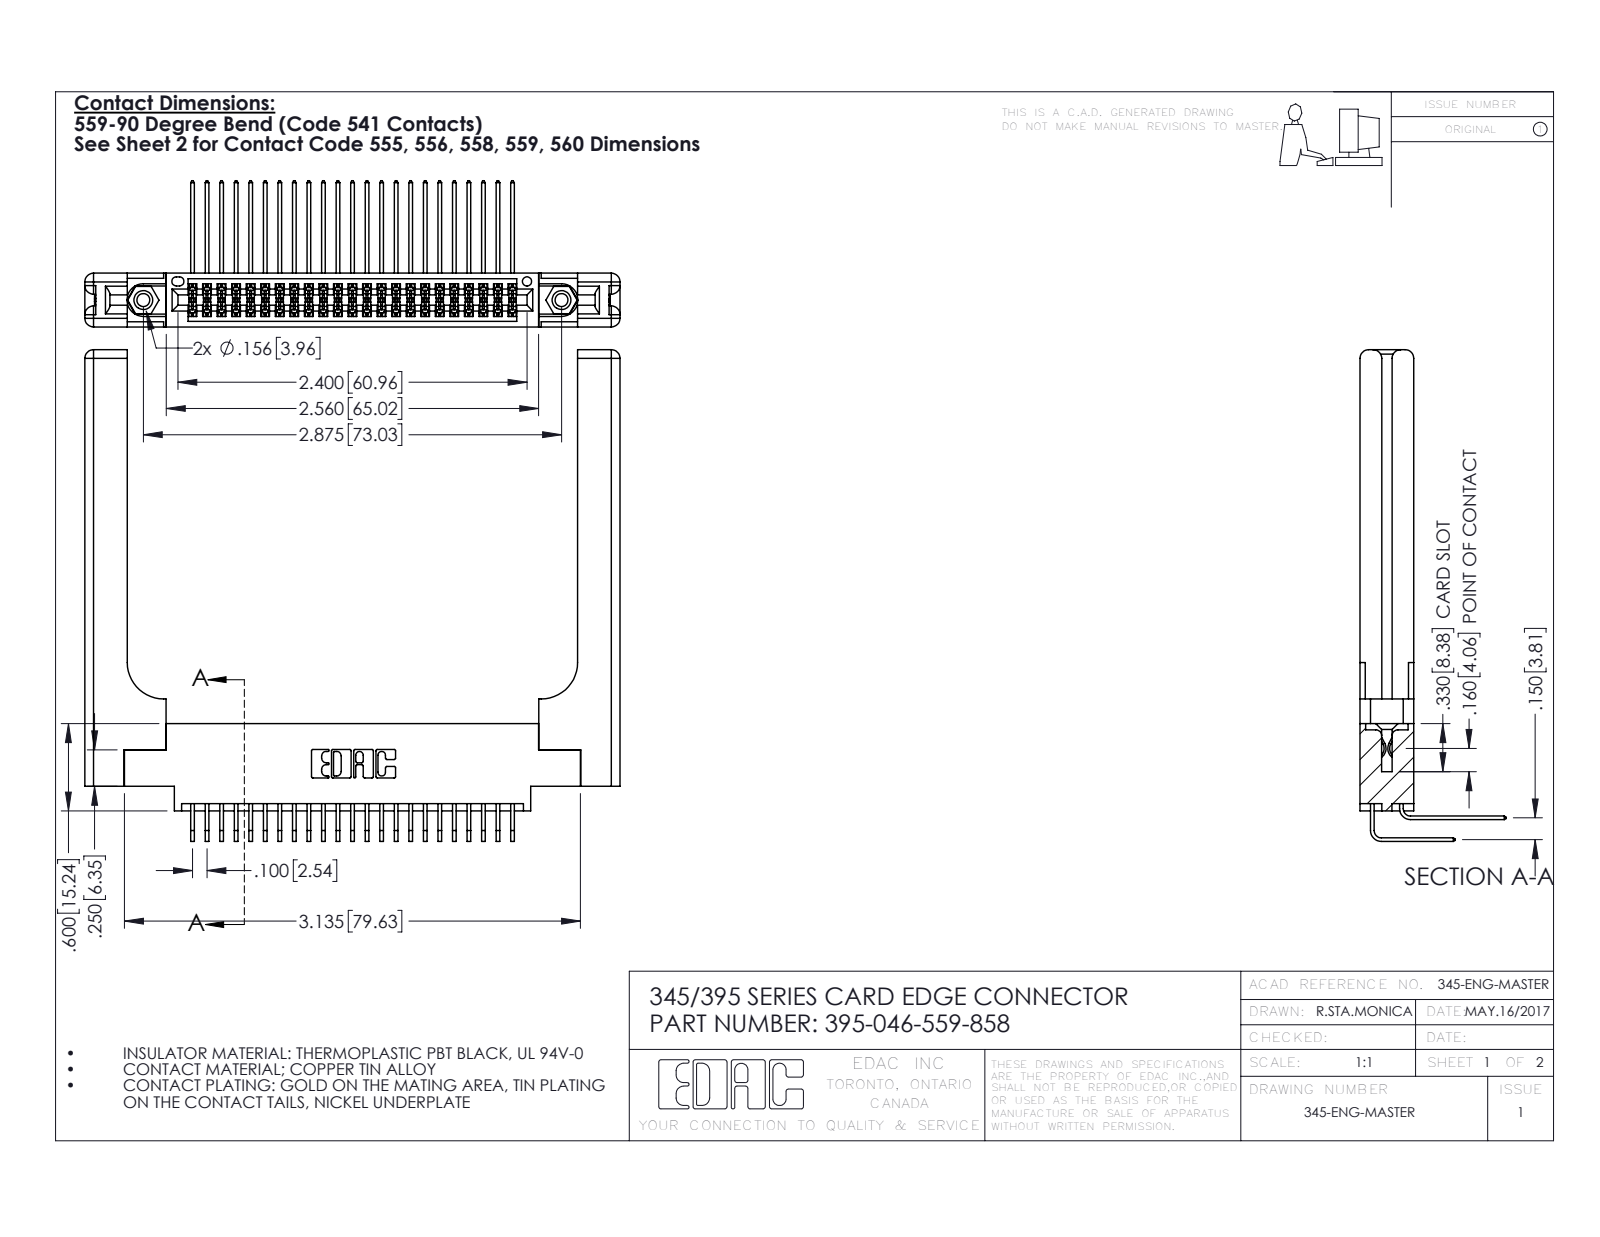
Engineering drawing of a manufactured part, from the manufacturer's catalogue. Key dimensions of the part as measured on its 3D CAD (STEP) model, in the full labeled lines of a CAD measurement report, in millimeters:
Part name (STEP PRODUCT): 345 Part_0.170 Offset - 0.156 Dia-TH; 345-220-058_345-220-058; 395-046-559-858; 345-292-001_558 559 Tail - 1 (+2 more)
STEP written by: SolidWorks 2016 (CONFIG_CONTROL_DESIGN)
Units: millimetres
Bodies: 51 solids, 2778 faces (1842 planar, 876 cylindrical, 60 other)
Overall size (bounding box): 93.4 × 85.8 × 25.5
Volume: 17 530 mm³ · Surface area: 19 460 mm²
Round holes (diameter × count): ⌀2.3 ×2, ⌀3.2 ×2, ⌀4 ×2, ⌀1.6 ×1
Round bosses / shafts (diameter × count): ⌀3.9 ×2
Partial cylindrical surfaces — rounded edges, fillets, slot ends (radius × count): R0.2 ×70, R0.3 ×22, R1.5 ×16, R0.2 ×6, R0.8 ×6, R0.7 ×3, R0.4 ×2, R0.5 ×2
Main face-to-face distances: 9.4, 1.8, 7.6, 3.8, 3.8, 2.5, 6.9, 0.6, 5.1, 2
Hole centre spacings: 6.9, 67.1, 73
